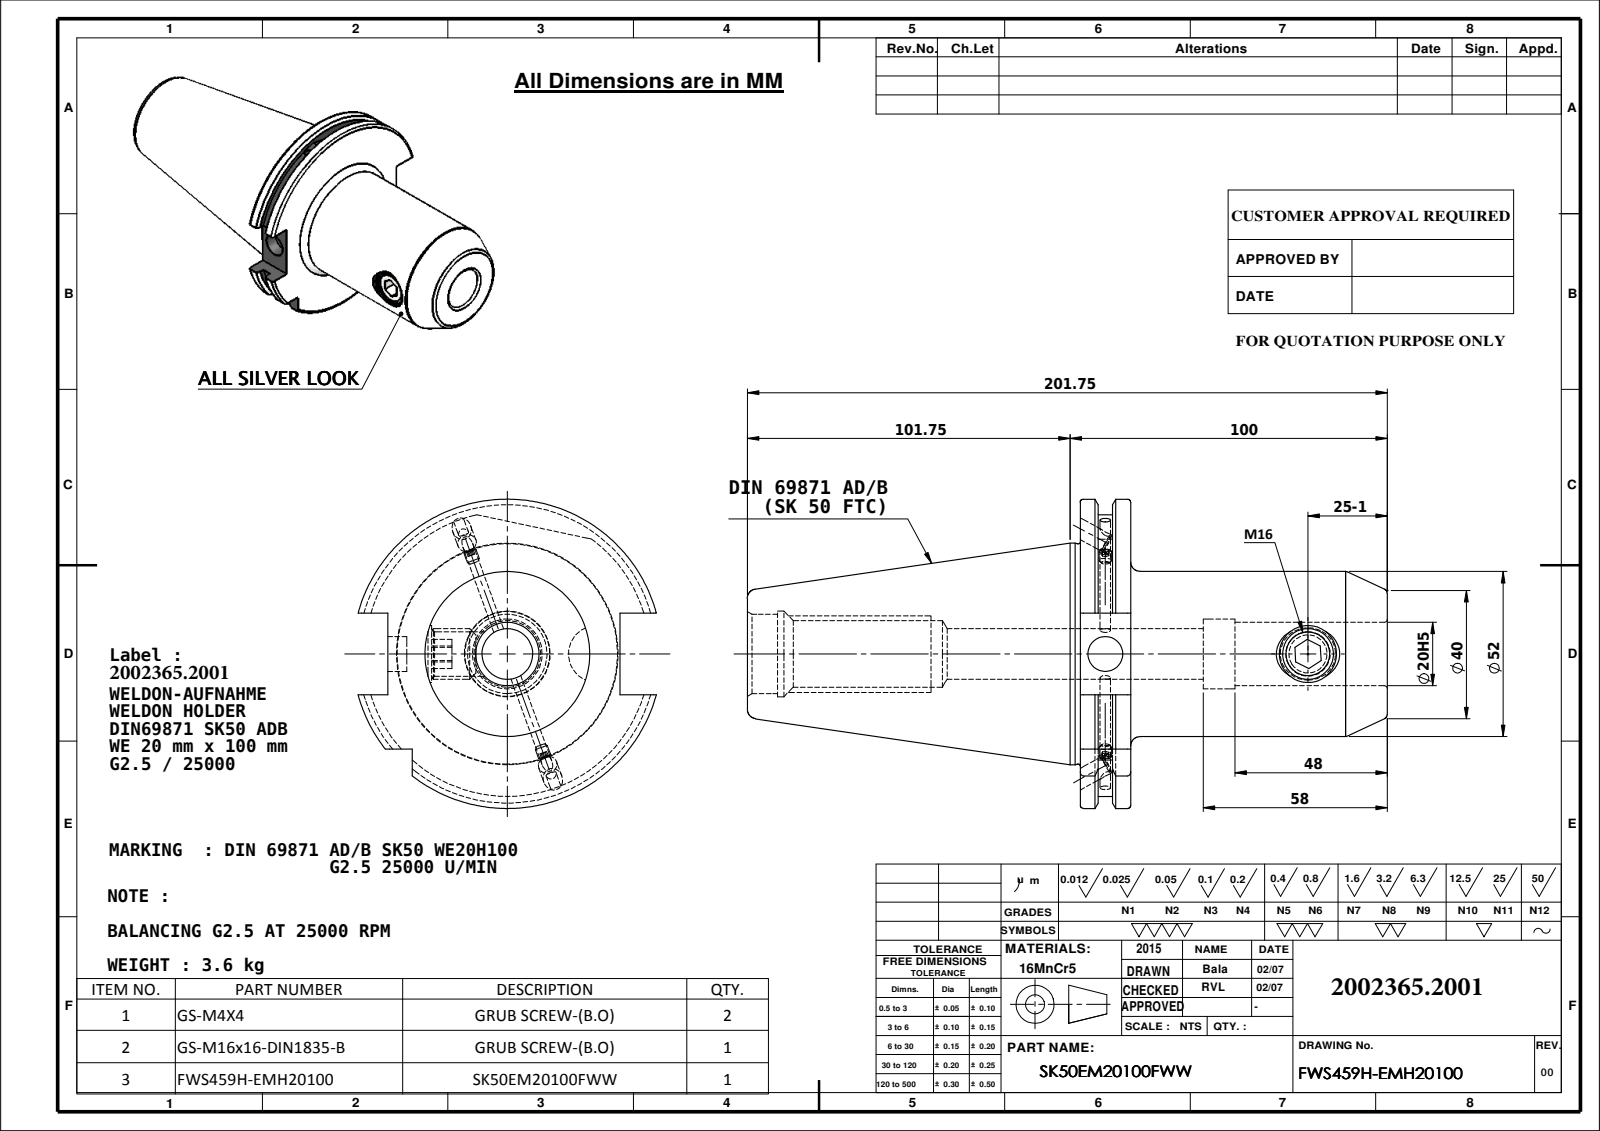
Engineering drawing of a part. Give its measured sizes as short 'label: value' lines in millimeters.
name: 91506-WE720100; SK50 EM 20 100 FTC WW; M16X16_ISO 4026 - M16 x 10-N; Copy of M4X4_DIN 913 - M4 x 4-N
written by: SolidWorks 2009 (CONFIG_CONTROL_DESIGN)
unit: mm
bodies: 4 solids, 168 faces (53 planar, 55 cylindrical, 60 other)
size: 201.75 × 97.5 × 94.05
volume: 467 826 mm³; area: 63 056 mm²
holes: 2× ⌀6, 1× ⌀3.3, 1× ⌀11, 1× ⌀14, 1× ⌀16, 1× ⌀18, 1× ⌀20, 1× ⌀21, 1× ⌀22, 1× ⌀25, 1× ⌀27
bosses: 2× ⌀4, 1× ⌀69.85, 1× ⌀69.45, 1× ⌀52, 1× ⌀16
rounds: 1× R44.9, 1× R48.75
face distances: 15.9, 96.8, 80.9, 5.66, 10.24, 91.14, 10.15, 4.49, 5.75, 86.65
hole spacings: 63.9
